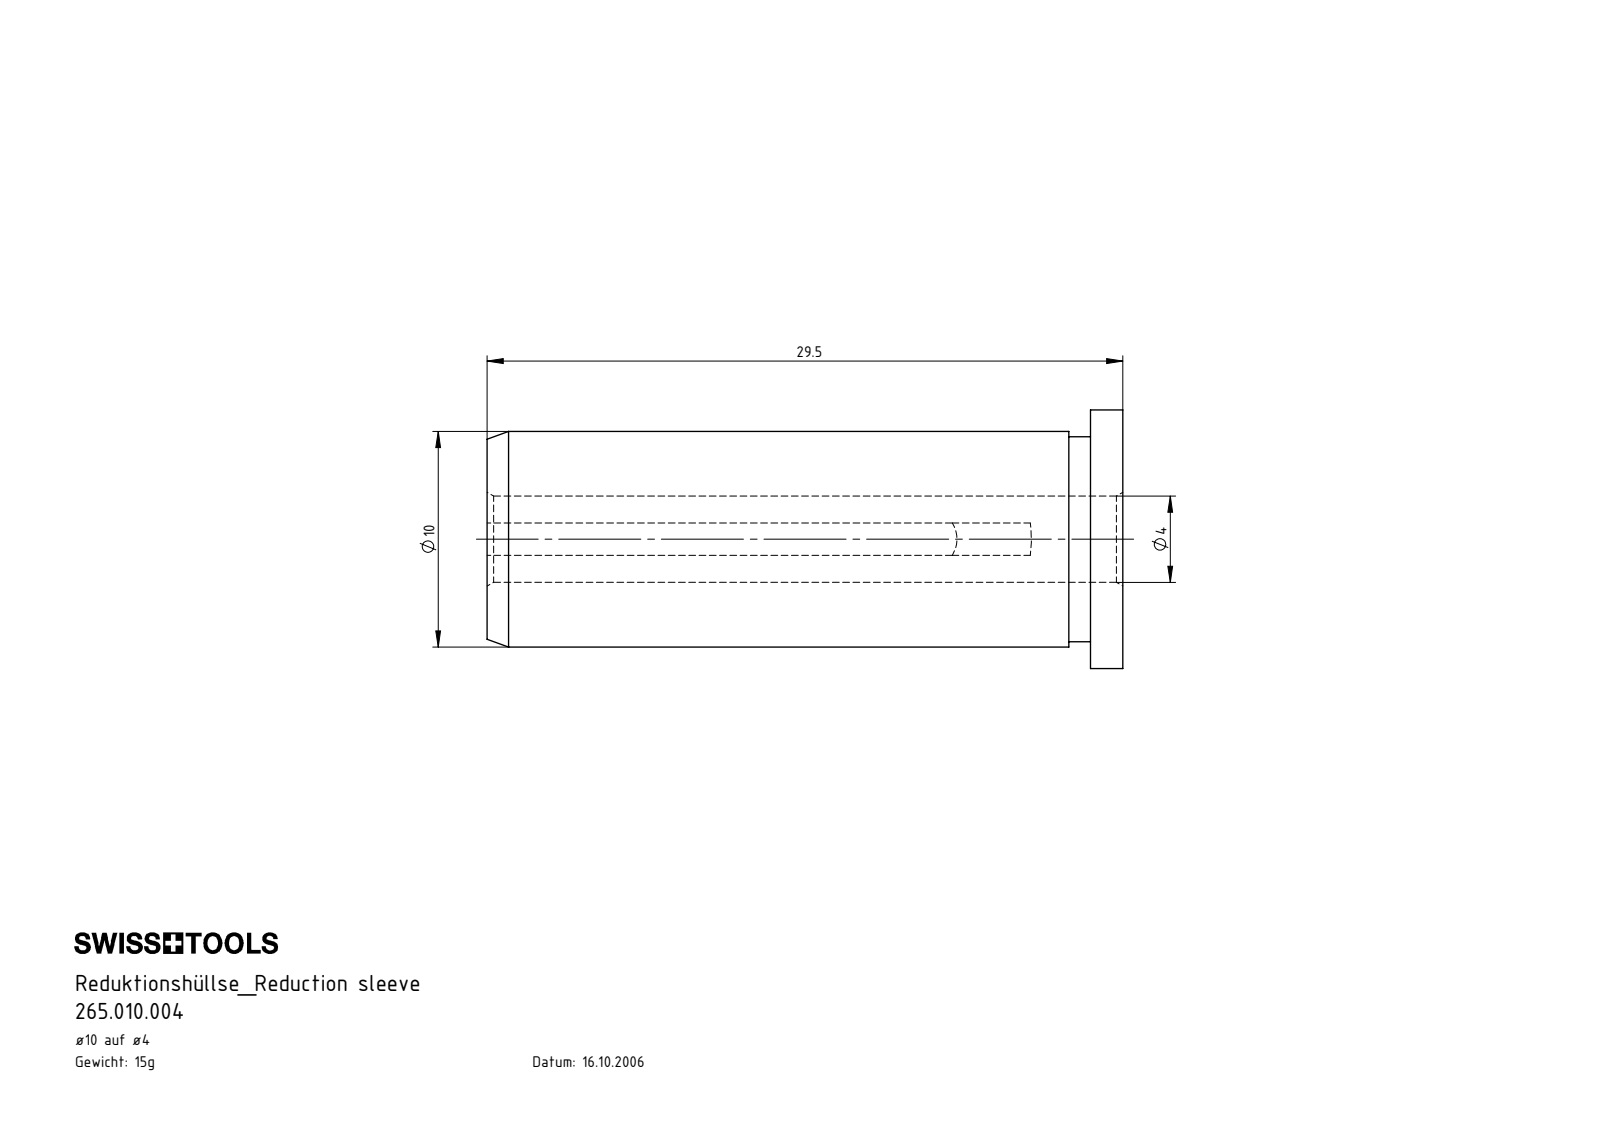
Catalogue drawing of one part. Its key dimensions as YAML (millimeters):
part_name: "265.010.004"
step_written_by: "SolidWorks 2017 (CONFIG_CONTROL_DESIGN)"
units: millimeters
bodies: {solids: 1, faces: 23, planar: 6, cylindrical: 9, other: 8}
overall_size: [29.5, 12, 12]
volume: 1877
surface_area: 1585
round_holes:
  - {diameter: 4, count: 1}
round_bosses_or_shafts:
  - {diameter: 12, count: 1}
  - {diameter: 10, count: 1}
  - {diameter: 9.5, count: 1}
partial_cylinders:
  - {radius: 20, count: 1}
face_to_face_distances: [1.5, 29.5, 28, 27, 1, 2.5]
